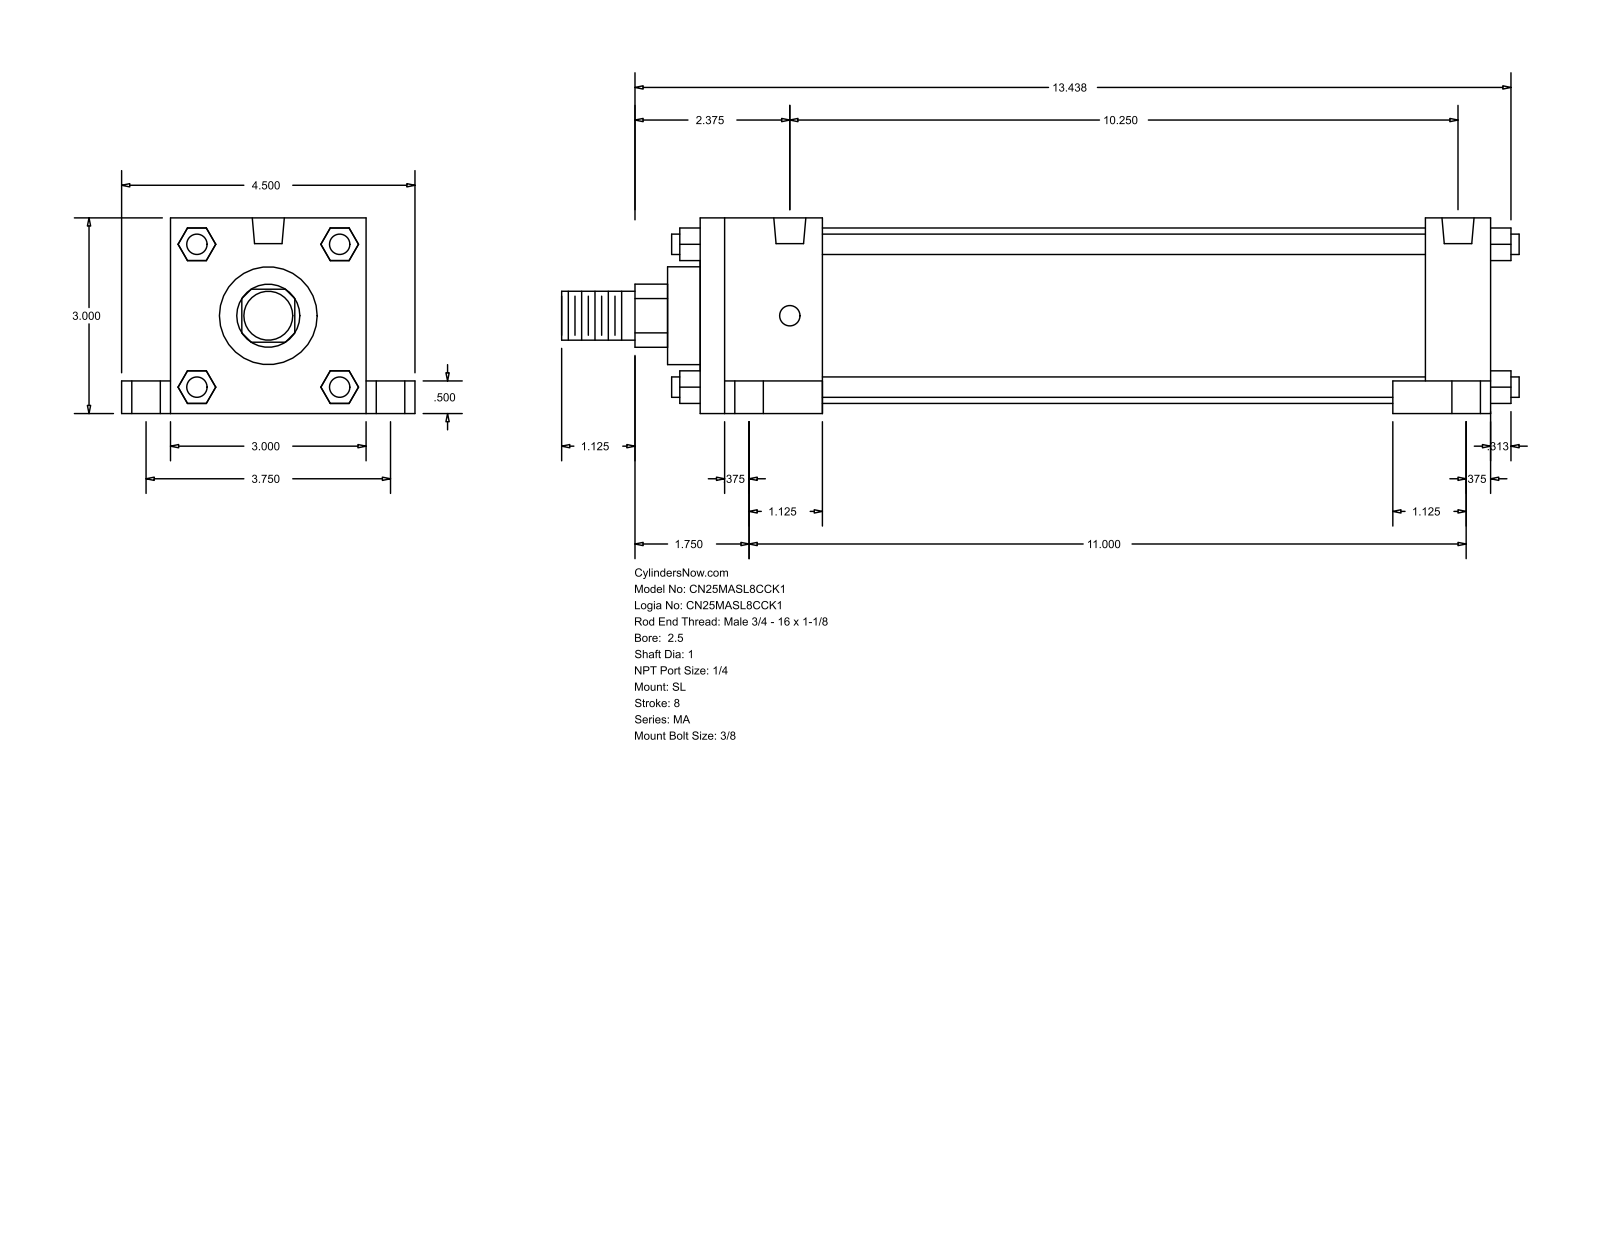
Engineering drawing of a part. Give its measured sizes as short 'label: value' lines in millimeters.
name: MA_SL__0250_1
written by: GSSL Pune (CONFIG_CONTROL_DESIGN)
unit: mm
bodies: 0 solids, 148 faces (112 planar, 36 cylindrical, 0 other)
size: 373.06 × 114.3 × 76.2
holes: 4× ⌀7.94, 4× ⌀11.11, 4× ⌀17.46, 2× ⌀12.49
bosses: 4× ⌀7.94, 1× ⌀68.33, 1× ⌀38.1, 1× ⌀25.4, 1× ⌀19.05
rounds: 1× R12.29
face distances: 76.2, 307.98, 12.7, 234.95, 25.4, 47.63, 260.35, 282.58, 19.05, 95.25
hole spacings: 47.73, 50.2, 95.24, 260.35, 267.79, 279.4, 280.3, 295.19
